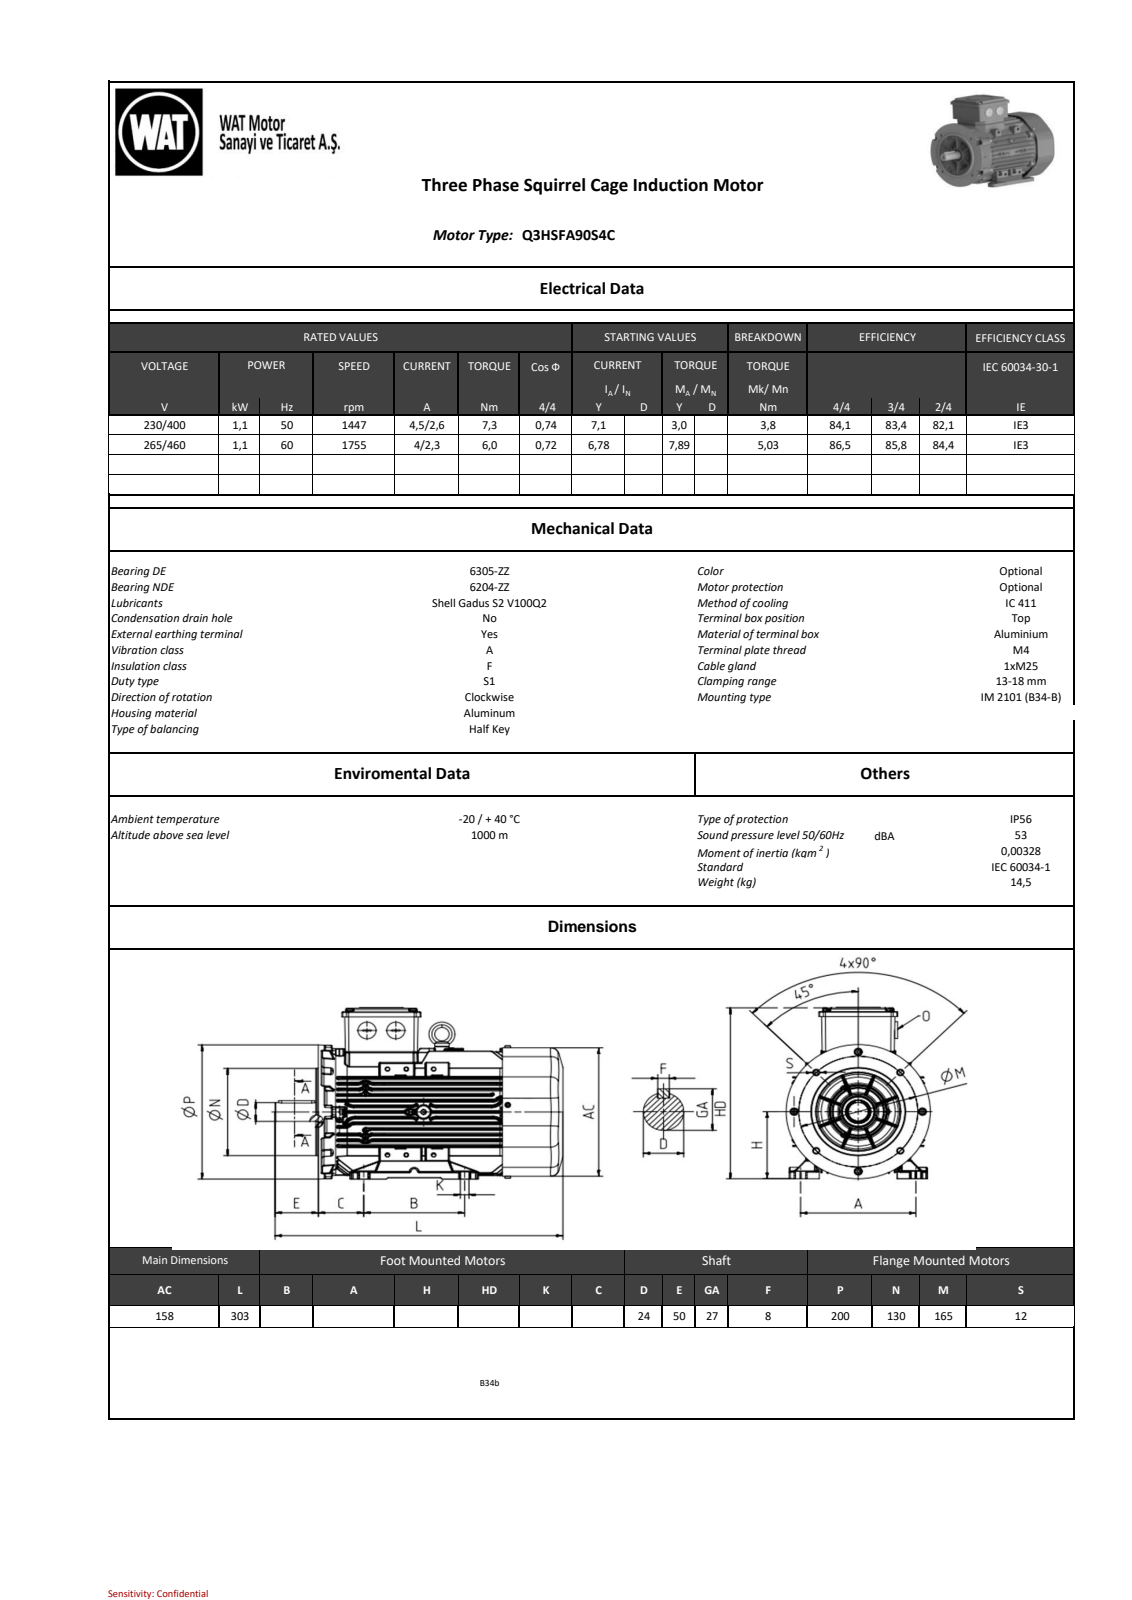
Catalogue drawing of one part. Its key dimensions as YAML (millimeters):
part_name: "model1_objects"
step_written_by: "SIEMENS PLM Software NX2206.8101 (AUTOMOTIVE_DESIGN)"
units: millimeters
bodies: {solids: 0, faces: 5431, planar: 1211, cylindrical: 2210, other: 2010}
overall_size: [303, 221.5, 200]
round_holes:
  - {diameter: 3.5, count: 4}
  - {diameter: 12, count: 4}
  - {diameter: 3, count: 2}
  - {diameter: 4.6, count: 2}
  - {diameter: 5.5, count: 1}
  - {diameter: 6.8, count: 1}
  - {diameter: 8, count: 1}
  - {diameter: 8.4, count: 1}
  - {diameter: 40, count: 1}
  - {diameter: 57.4, count: 1}
round_bosses_or_shafts:
  - {diameter: 6, count: 4}
  - {diameter: 8.33, count: 3}
  - {diameter: 146.5, count: 1}
  - {diameter: 130, count: 1}
  - {diameter: 68.9, count: 1}
  - {diameter: 61, count: 1}
  - {diameter: 25, count: 1}
  - {diameter: 24.07, count: 1}
partial_cylinders:
  - {radius: 1, count: 575}
  - {radius: 0.5, count: 493}
  - {radius: 0.8, count: 317}
  - {radius: 2, count: 52}
  - {radius: 1.5, count: 32}
  - {radius: 0.5, count: 23}
  - {radius: 2.5, count: 16}
  - {radius: 4, count: 14}
face_to_face_distances: [1, 138, 4, 6, 35.5, 158, 11, 36.5, 20, 169]
hole_center_spacings: [82.51, 116.68, 20, 25.5, 58.25, 79.8, 82.47, 82.54]
